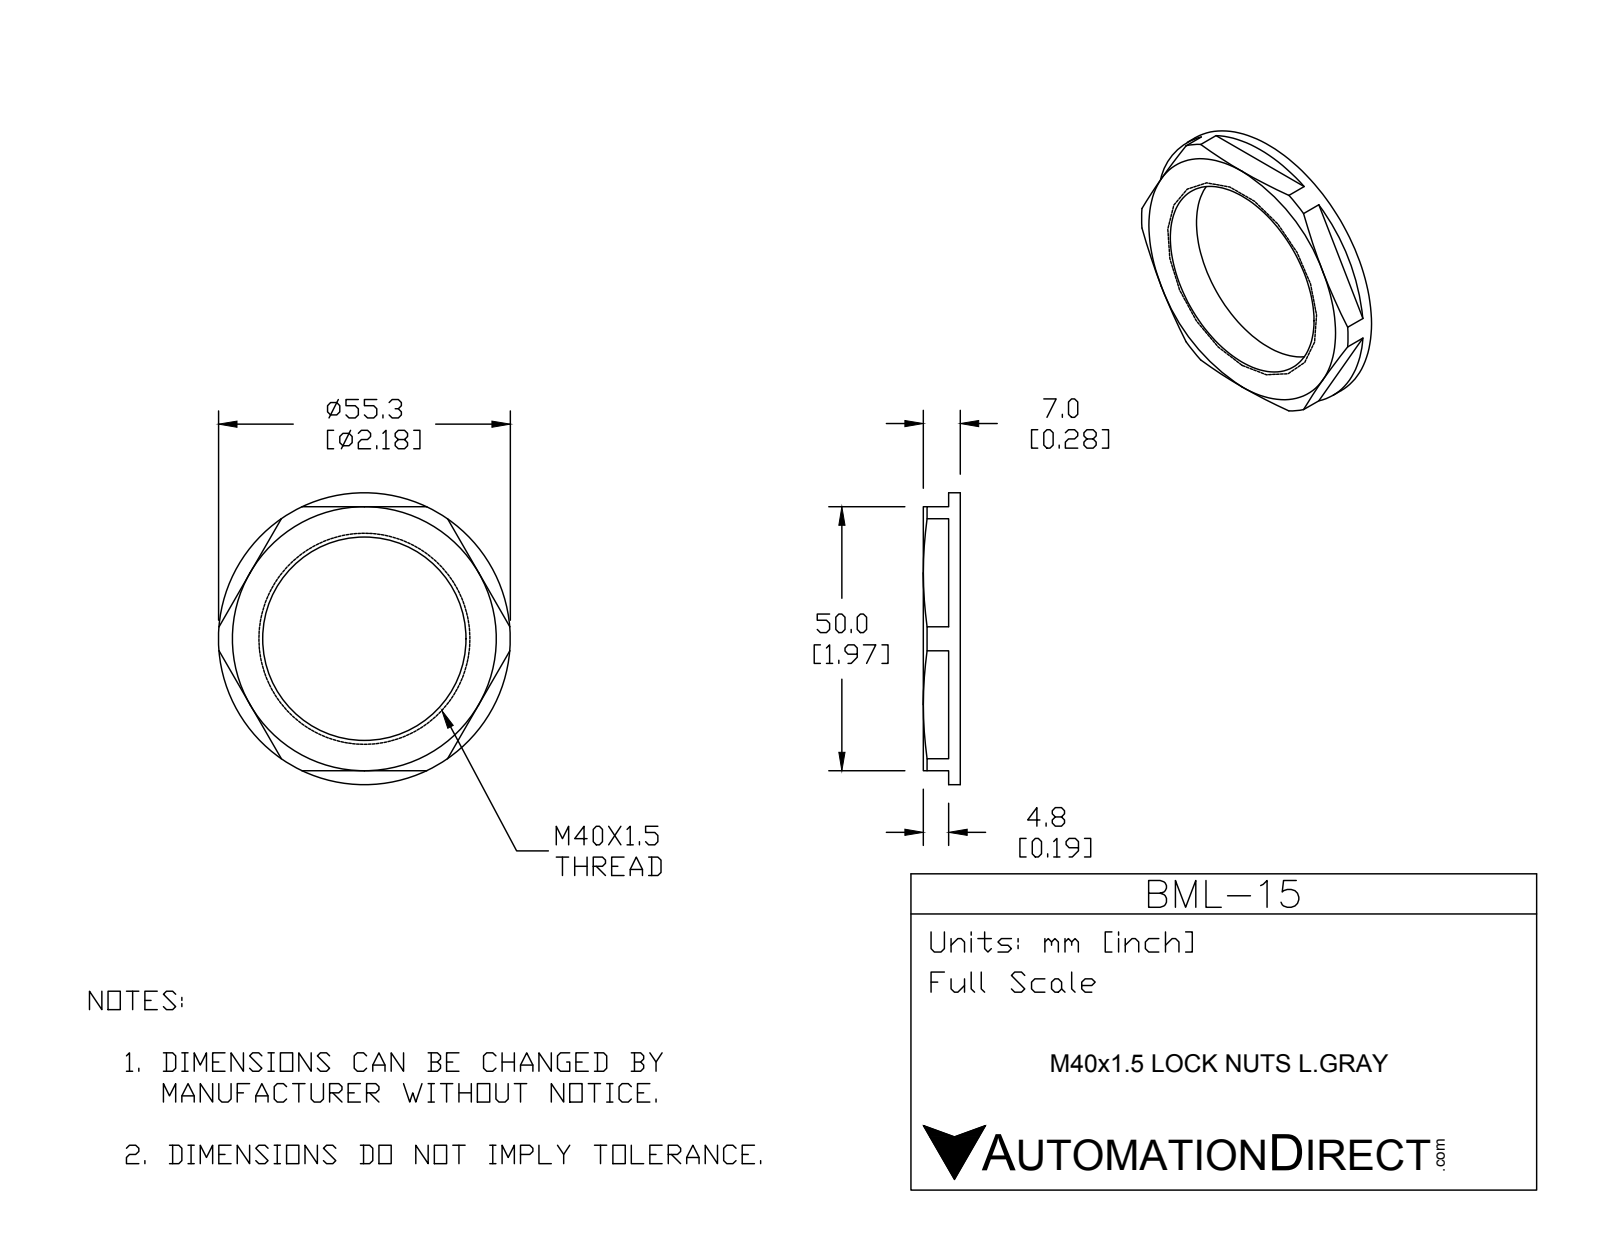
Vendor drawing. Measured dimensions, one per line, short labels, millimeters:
name: BML-15
written by: SolidWorks 2015 (CONFIG_CONTROL_DESIGN)
unit: mm
bodies: 1 solid, 33 faces (17 planar, 10 cylindrical, 6 other)
size: 55.3 × 55.3 × 7
volume: 7 398 mm³; area: 4 473 mm²
holes: 3× ⌀1.5, 1× ⌀38.5
bosses: 1× ⌀55.3
face distances: 7, 50, 2.2, 4.8, 1.9, 6.7
hole spacings: 26.2, 45.38
